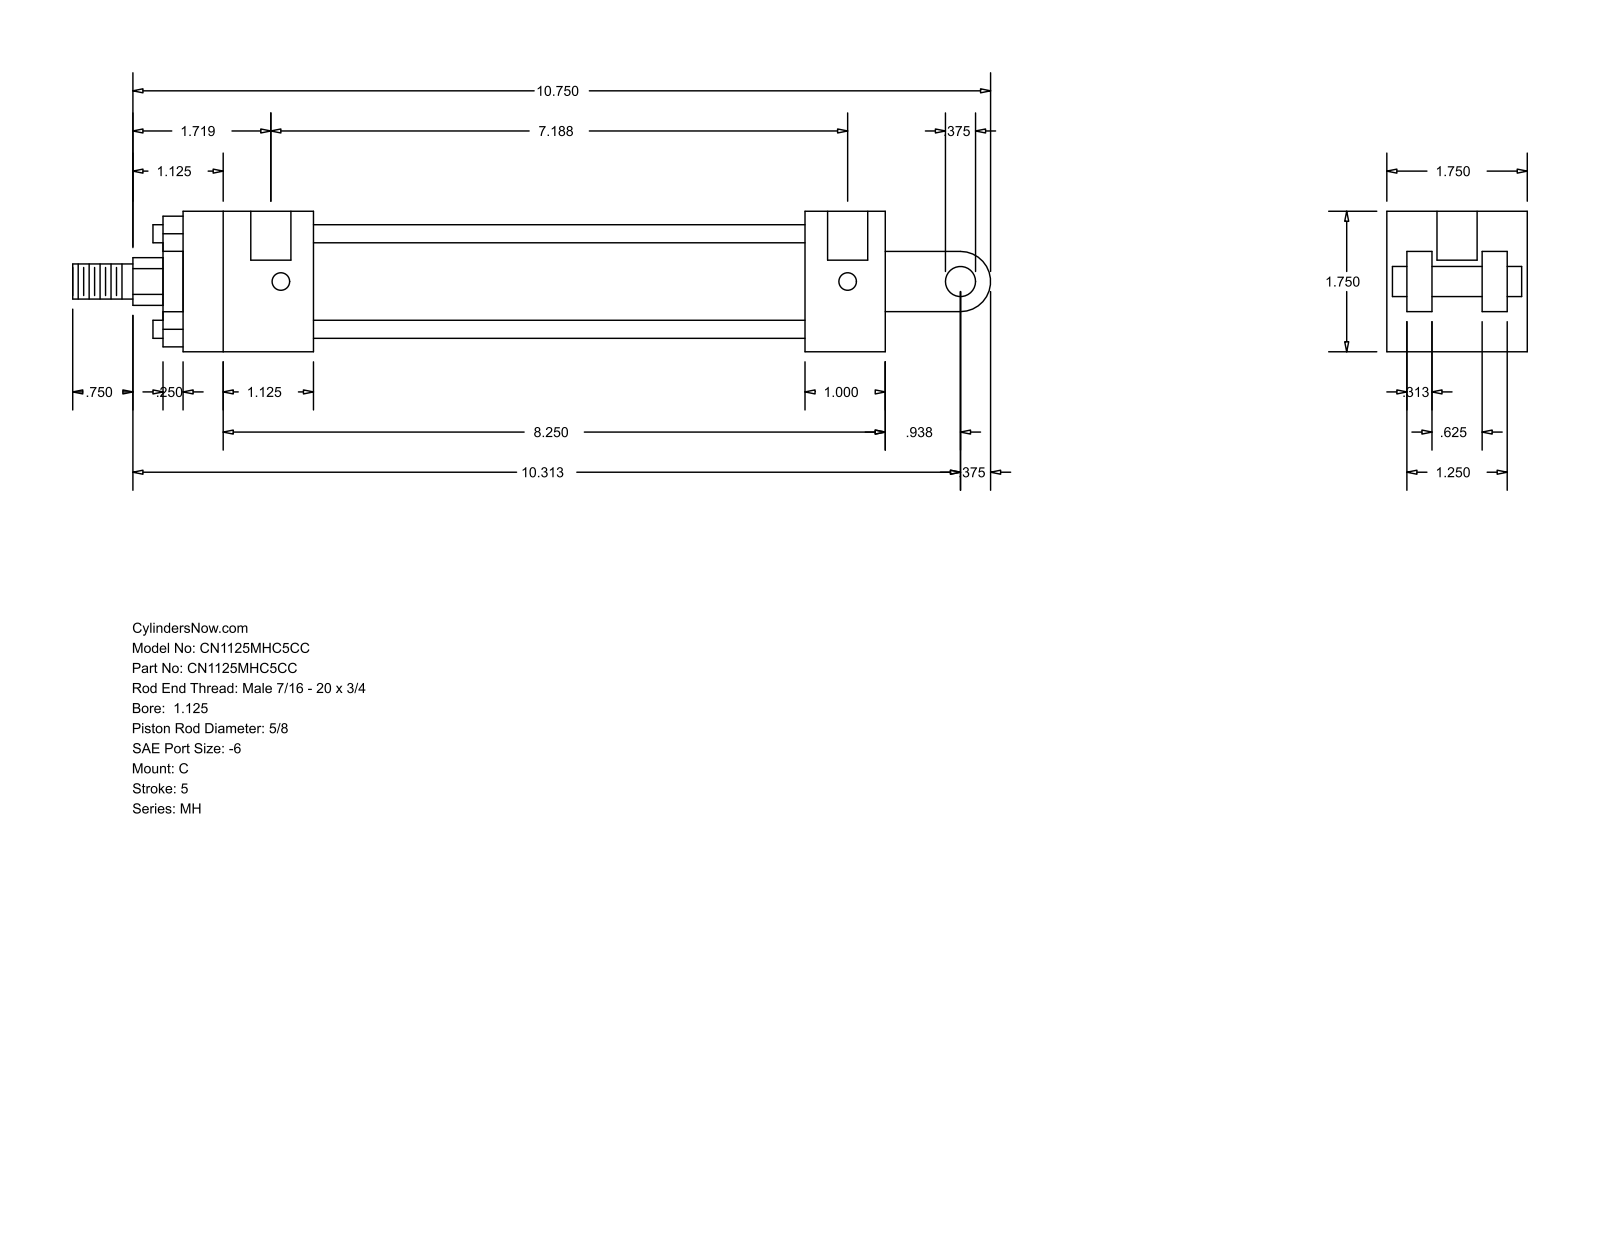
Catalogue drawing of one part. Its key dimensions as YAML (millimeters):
part_name: "MH_C__0112_0.625"
step_written_by: "GSSL Pune (CONFIG_CONTROL_DESIGN)"
units: millimeters
bodies: {solids: 0, faces: 99, planar: 70, cylindrical: 29, other: 0}
overall_size: [290.51, 44.45, 44.45]
round_holes:
  - {diameter: 5.56, count: 4}
  - {diameter: 12.7, count: 2}
round_bosses_or_shafts:
  - {diameter: 5.71, count: 4}
  - {diameter: 34.92, count: 1}
  - {diameter: 28.57, count: 1}
  - {diameter: 15.88, count: 1}
  - {diameter: 11.11, count: 1}
  - {diameter: 9.53, count: 1}
partial_cylinders:
  - {radius: 7.54, count: 1}
  - {radius: 9.53, count: 1}
face_to_face_distances: [44.46, 6.35, 31.76, 14.29, 25.4, 30.17, 38.11, 7.94, 23.82, 12.7]
hole_center_spacings: [179.39, 3.17, 182.56]
